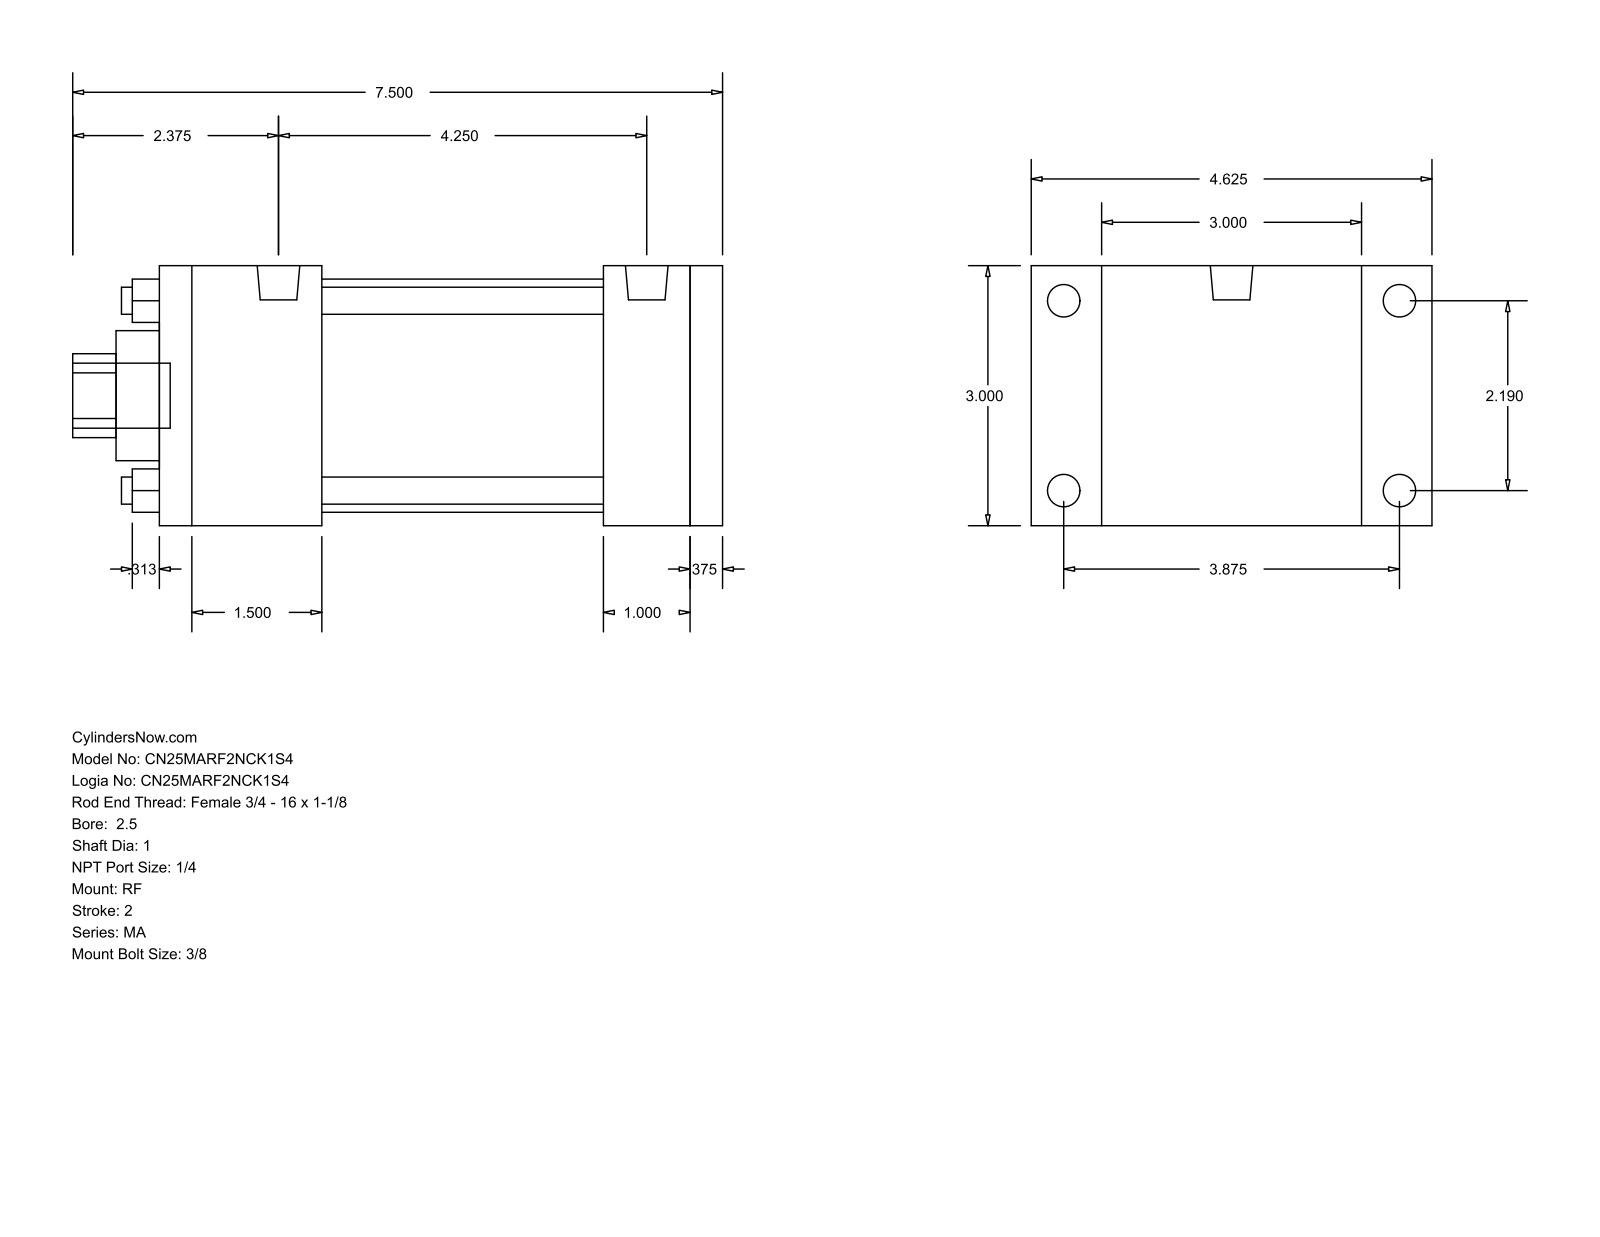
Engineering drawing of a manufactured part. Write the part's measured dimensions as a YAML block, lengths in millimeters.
part_name: "MA_RF__0250_1"
step_written_by: "GSSL Pune (CONFIG_CONTROL_DESIGN)"
units: millimeters
bodies: {solids: 0, faces: 92, planar: 64, cylindrical: 28, other: 0}
overall_size: [190.5, 117.47, 76.2]
round_holes:
  - {diameter: 7.94, count: 4}
  - {diameter: 25.4, count: 1}
  - {diameter: 38.1, count: 1}
  - {diameter: 68.33, count: 1}
round_bosses_or_shafts:
  - {diameter: 9.53, count: 4}
  - {diameter: 7.94, count: 4}
  - {diameter: 12.49, count: 2}
  - {diameter: 19.05, count: 1}
partial_cylinders:
  - {radius: 12.29, count: 1}
face_to_face_distances: [76.2, 165.1, 155.57, 9.53, 25.4, 47.63, 130.17, 82.54, 107.94, 117.47]
hole_center_spacings: [39.33, 55.62, 78.66]
